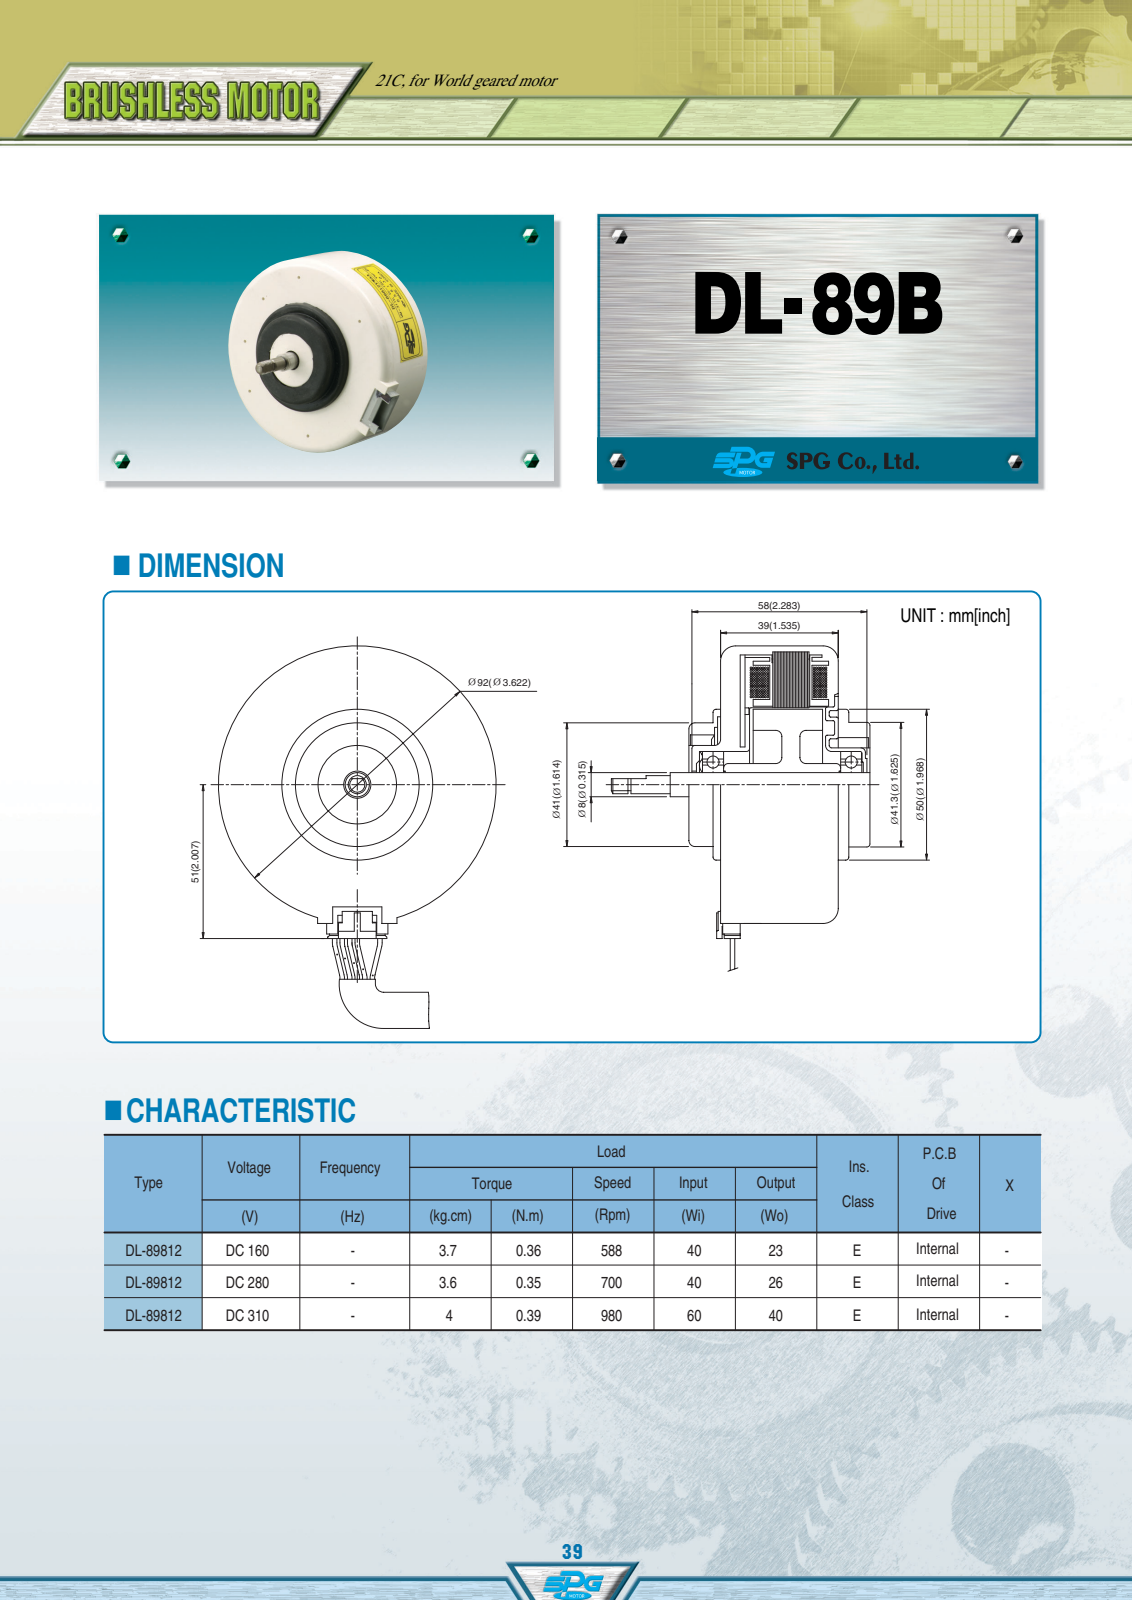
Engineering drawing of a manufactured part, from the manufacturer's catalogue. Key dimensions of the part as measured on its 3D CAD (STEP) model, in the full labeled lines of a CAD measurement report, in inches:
Part name (STEP PRODUCT): 89812_BMC
STEP written by: Autodesk Inventor 2011 (AUTOMOTIVE_DESIGN)
Units: inches
Bodies: 1 solid, 114 faces (77 planar, 19 cylindrical, 18 other)
Overall size (bounding box): 3.72 × 3.622 × 3.319
Volume: 17.34 in³ · Surface area: 51.78 in²
Round holes (diameter × count): ⌀0.354 ×1, ⌀0.961 ×1, ⌀1.024 ×1, ⌀1.197 ×1, ⌀1.496 ×1, ⌀1.772 ×1, ⌀1.933 ×1
Round bosses / shafts (diameter × count): ⌀3.622 ×1, ⌀2.303 ×1, ⌀1.969 ×1, ⌀1.764 ×1, ⌀1.626 ×1, ⌀1.614 ×1, ⌀0.685 ×1, ⌀0.315 ×1
Main face-to-face distances: 1.535, 0.039, 1.949, 0.413, 0.335, 0.374, 0.276, 2.047, 0.098, 1.988
